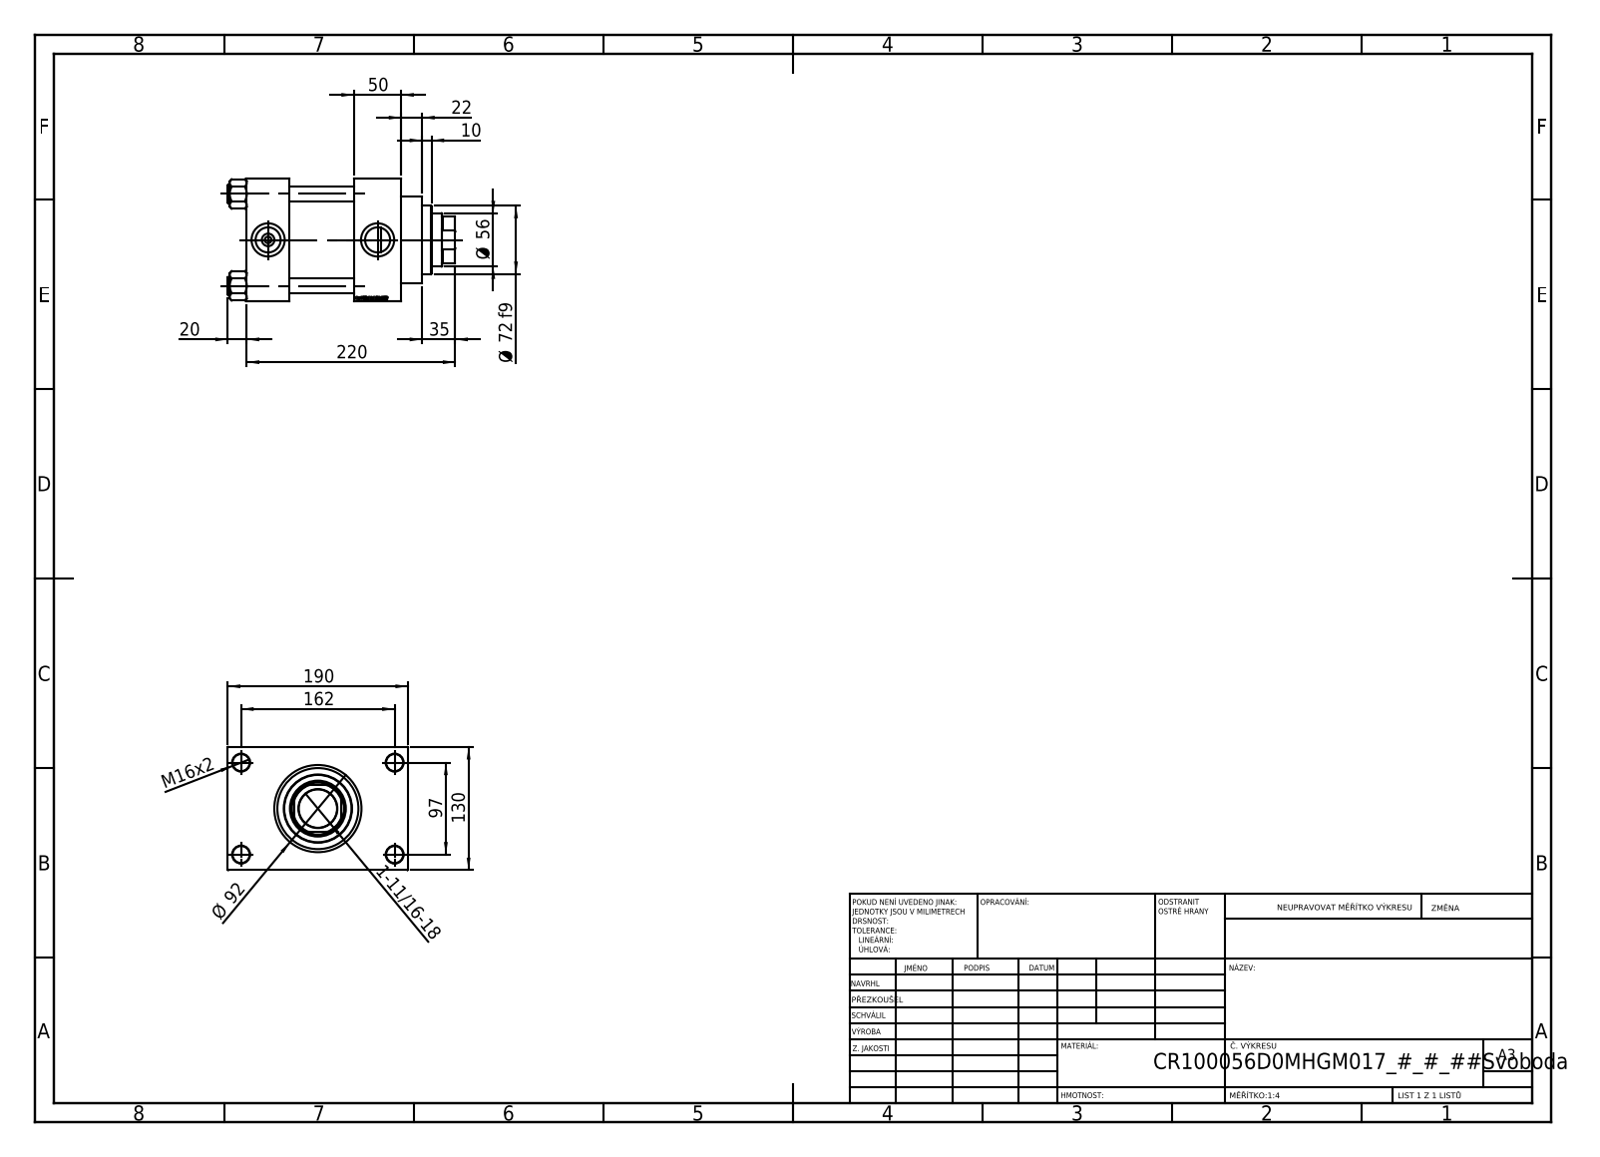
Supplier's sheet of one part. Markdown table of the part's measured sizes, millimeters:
| quantity | value |
| --- | --- |
| part name | V215CR_D_Body; V215CR_D_TYCINKA; V215_VC_A; V215CR_VCP_D (+1 more) |
| STEP written by | SolidWorks 2019 (CONFIG_CONTROL_DESIGN) |
| units | millimeters |
| bodies | 11 solids, 1151 faces (545 planar, 88 cylindrical, 518 other) |
| overall size | 240 × 190 × 130 |
| volume | 2 615 000 mm³ |
| surface area | 359 291 mm² |
| round holes (diameter × count) | 16 × 4, 18 × 4, 7 × 2, 26.44 × 2, 35 × 2, 40.5 × 1, 56 × 1, 59 × 1, 76 × 1, 85.5 × 1, 100 × 1 |
| round bosses / shafts (diameter × count) | 19 × 4, 106 × 1, 92 × 1, 72 × 1 |
| partial cylindrical surfaces (radius × count) | 27 × 1 |
| main face-to-face distances | 130, 50, 45, 68, 113, 118, 163, 30, 160, 190 |
| hole center spacings | 32.55, 68.52, 94.41, 96.9, 102.27, 129.45, 161.73, 97 |
